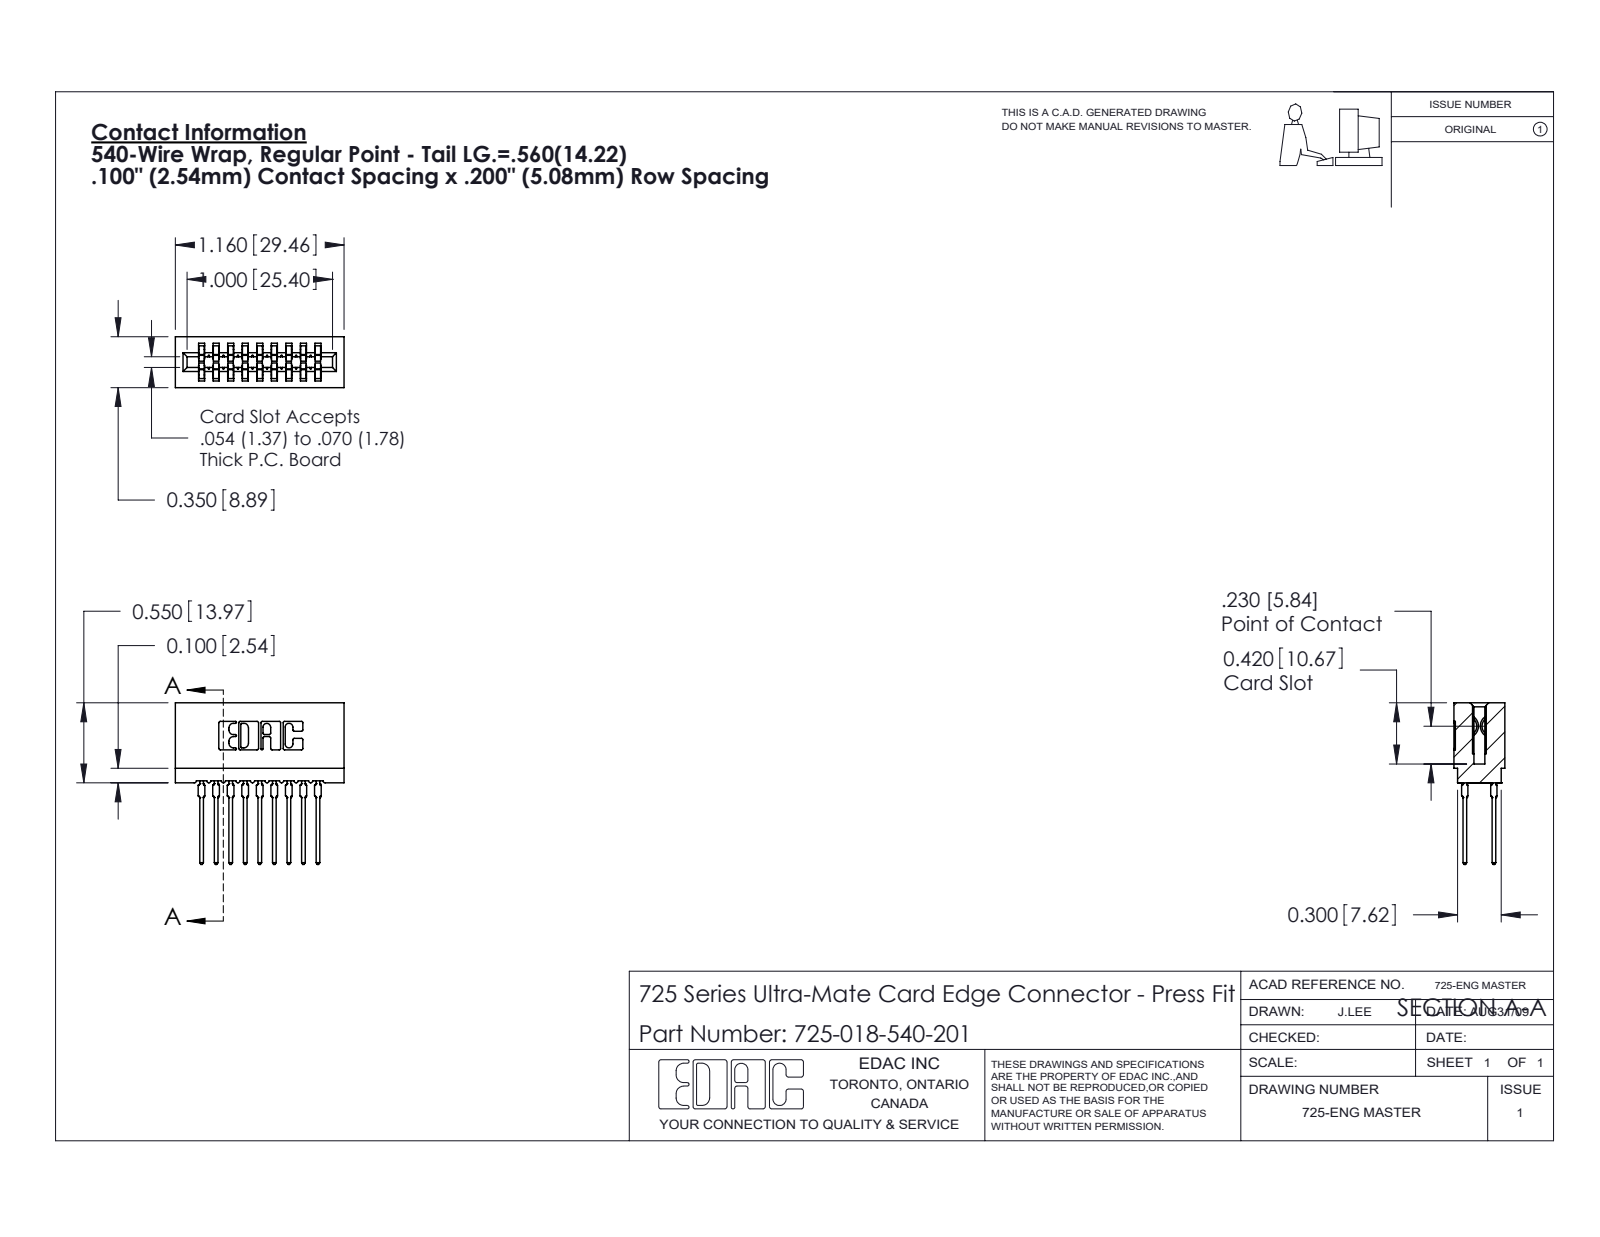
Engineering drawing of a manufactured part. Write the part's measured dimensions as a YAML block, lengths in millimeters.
part_name: "745-292-001_540; 725 Part_Insulator Option - 01; 725-018-540-201"
step_written_by: "SolidWorks 2020 (CONFIG_CONTROL_DESIGN)"
units: millimeters
bodies: {solids: 19, faces: 1706, planar: 883, cylindrical: 355, other: 468}
overall_size: [29.5, 28.2, 8.9]
volume: 2560
surface_area: 4902
partial_cylinders:
  - {radius: 0.5, count: 36}
  - {radius: 0.3, count: 22}
  - {radius: 0.4, count: 18}
  - {radius: 0.1, count: 8}
  - {radius: 0.3, count: 8}
  - {radius: 0.2, count: 6}
  - {radius: 0.8, count: 6}
  - {radius: 0.7, count: 3}
face_to_face_distances: [5.1, 2.5, 7.6, 10.2, 1.1, 12.7, 3.6, 1.5, 6.1, 4]
